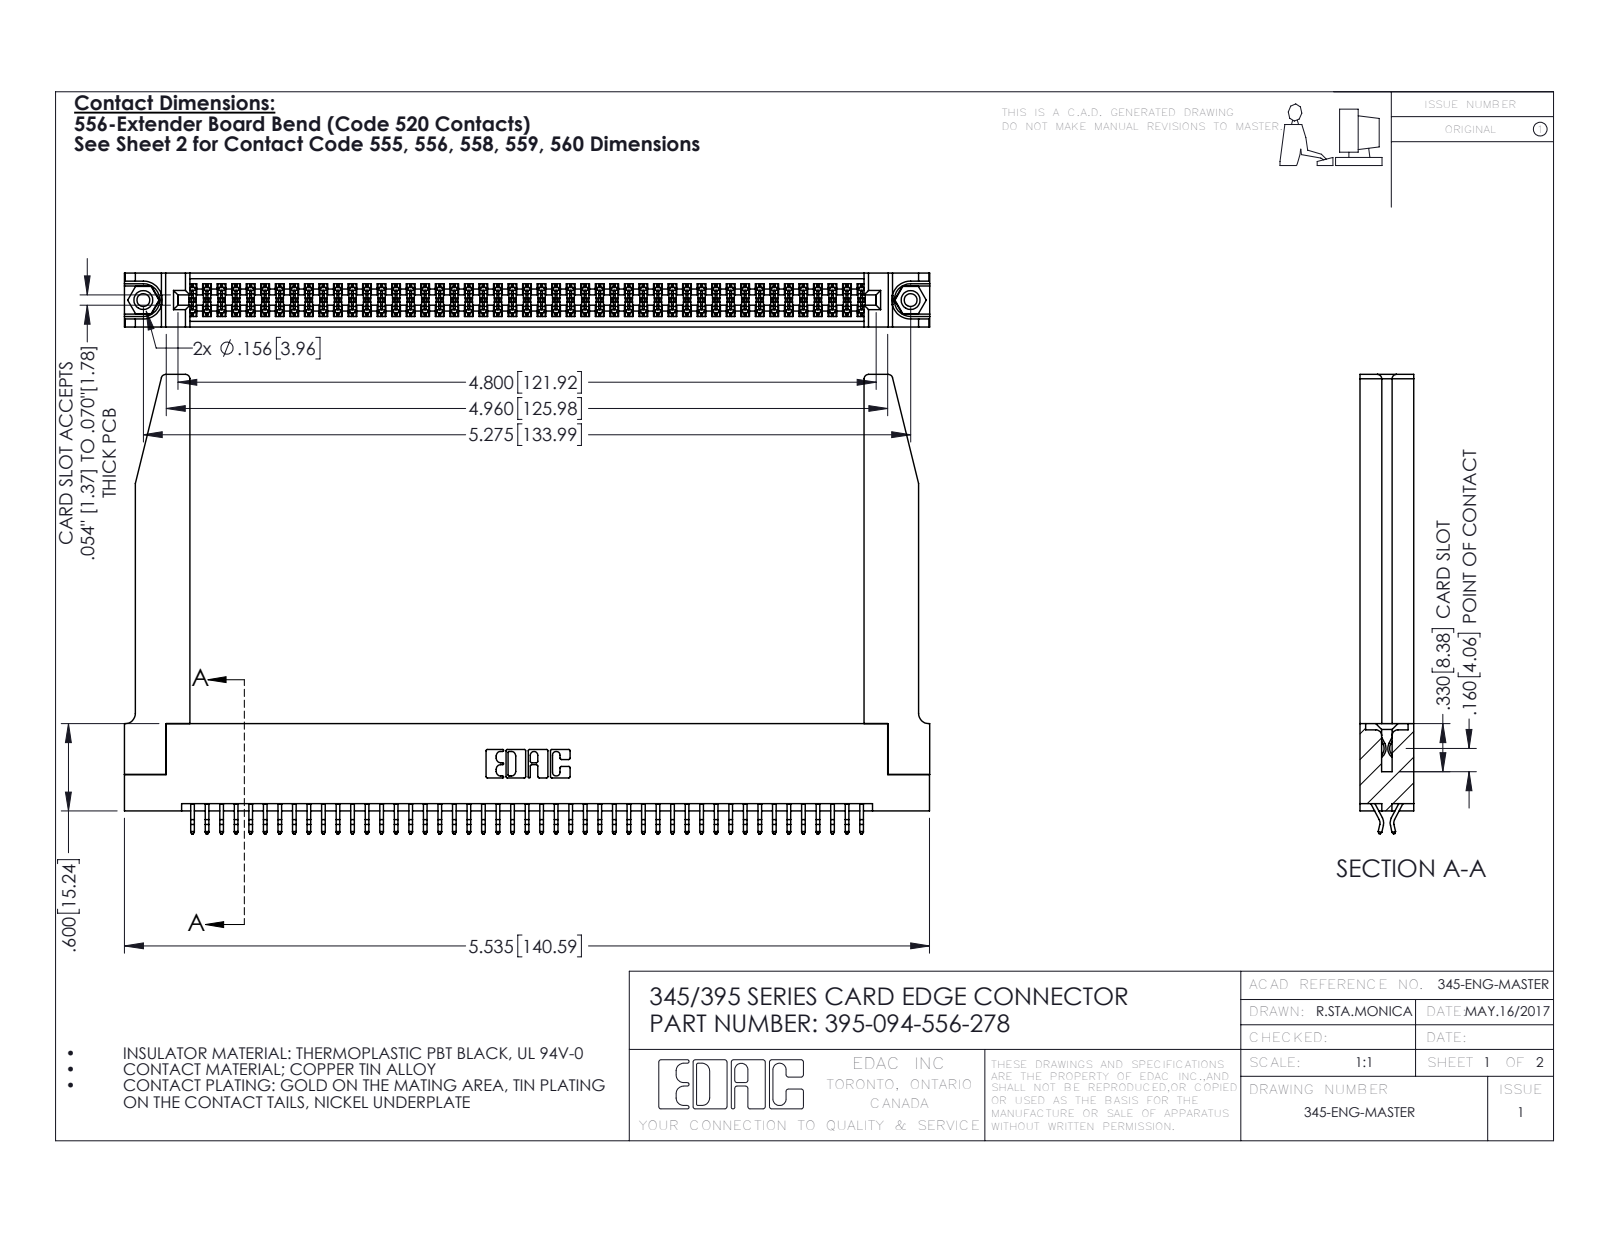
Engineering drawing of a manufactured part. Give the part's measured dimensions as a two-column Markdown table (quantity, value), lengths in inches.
| quantity | value |
| --- | --- |
| part name | 395-094-556-278; 345-220-078_345-220-078; 345 Part_Flush Mounting Lugs - 0.156 Dia-TH; 345-292-001_556 Tail (+1 more) |
| STEP written by | SolidWorks 2016 (CONFIG_CONTROL_DESIGN) |
| units | inches |
| bodies | 99 solids, 5624 faces (3700 planar, 1872 cylindrical, 52 other) |
| overall size | 5.536 × 3.157 × 0.37 |
| volume | 1.31 in³ |
| surface area | 42.02 in² |
| round holes (diameter × count) | 0.089 × 2, 0.125 × 2, 0.156 × 2, 0.064 × 1 |
| round bosses / shafts (diameter × count) | 0.155 × 2 |
| partial cylindrical surfaces (radius × count) | 0.006 × 141, 0.01 × 22, 0.03 × 8, 0.007 × 6, 0.031 × 6, 0.026 × 3, 0.01 × 2, 0.014 × 2 |
| main face-to-face distances | 0.37, 0.072, 0.298, 0.2, 0.025, 0.098, 0.272, 0.225, 0.148, 0.15 |
| hole center spacings | 0.27, 5.039, 5.275 |
